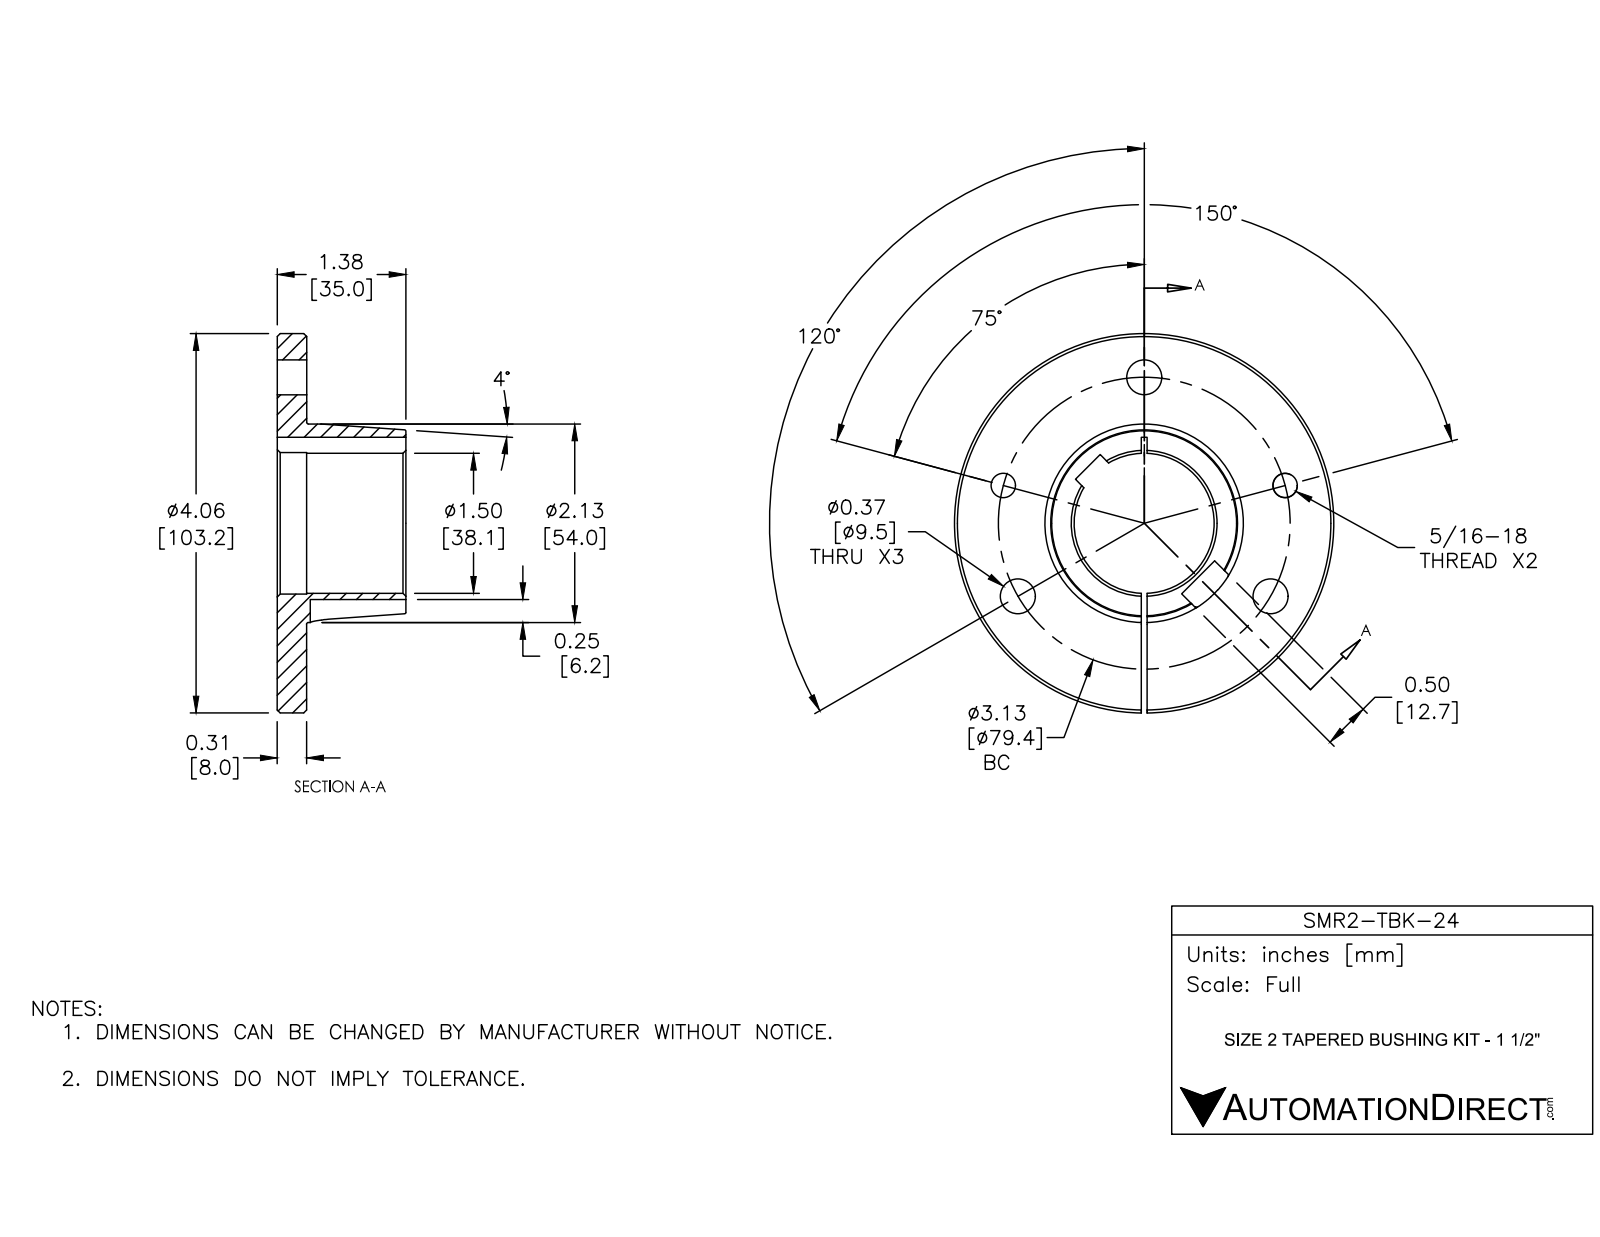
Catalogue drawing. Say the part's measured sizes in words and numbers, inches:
The part is named "SMR2-TBK-24". Its 3-D file was written by "SolidWorks 2016 (AUTOMOTIVE_DESIGN)". It is 1 solid with 124 faces: 18 planar, 79 cylindrical and 27 other. Overall it measures 4.063 by 4.062 by 1.378 inches. Its volume is 4.841 cubic inches and its surface area 42 square inches. Round holes: 3 of diameter 0.374, 2 of diameter 0.32, 1 of diameter 0.26, 1 of diameter 1.5, 1 of diameter 1.516. Round bosses or shafts: 1 of diameter 4.063, 1 of diameter 2.126. Partial cylindrical surfaces (rounded edges, fillets, slot ends): 2 of radius 0.13, 2 of radius 0.197. The main face-to-face distances are 0.315, 1.378, 1.063, 0.063, 1.672, 0.063, 0.437, 0.375, 0.5, 0.354. The hole center spacings are 1.563, 2.707, 1.196, 1.563, 1.563, 1.903, 1.904, 3.02.
